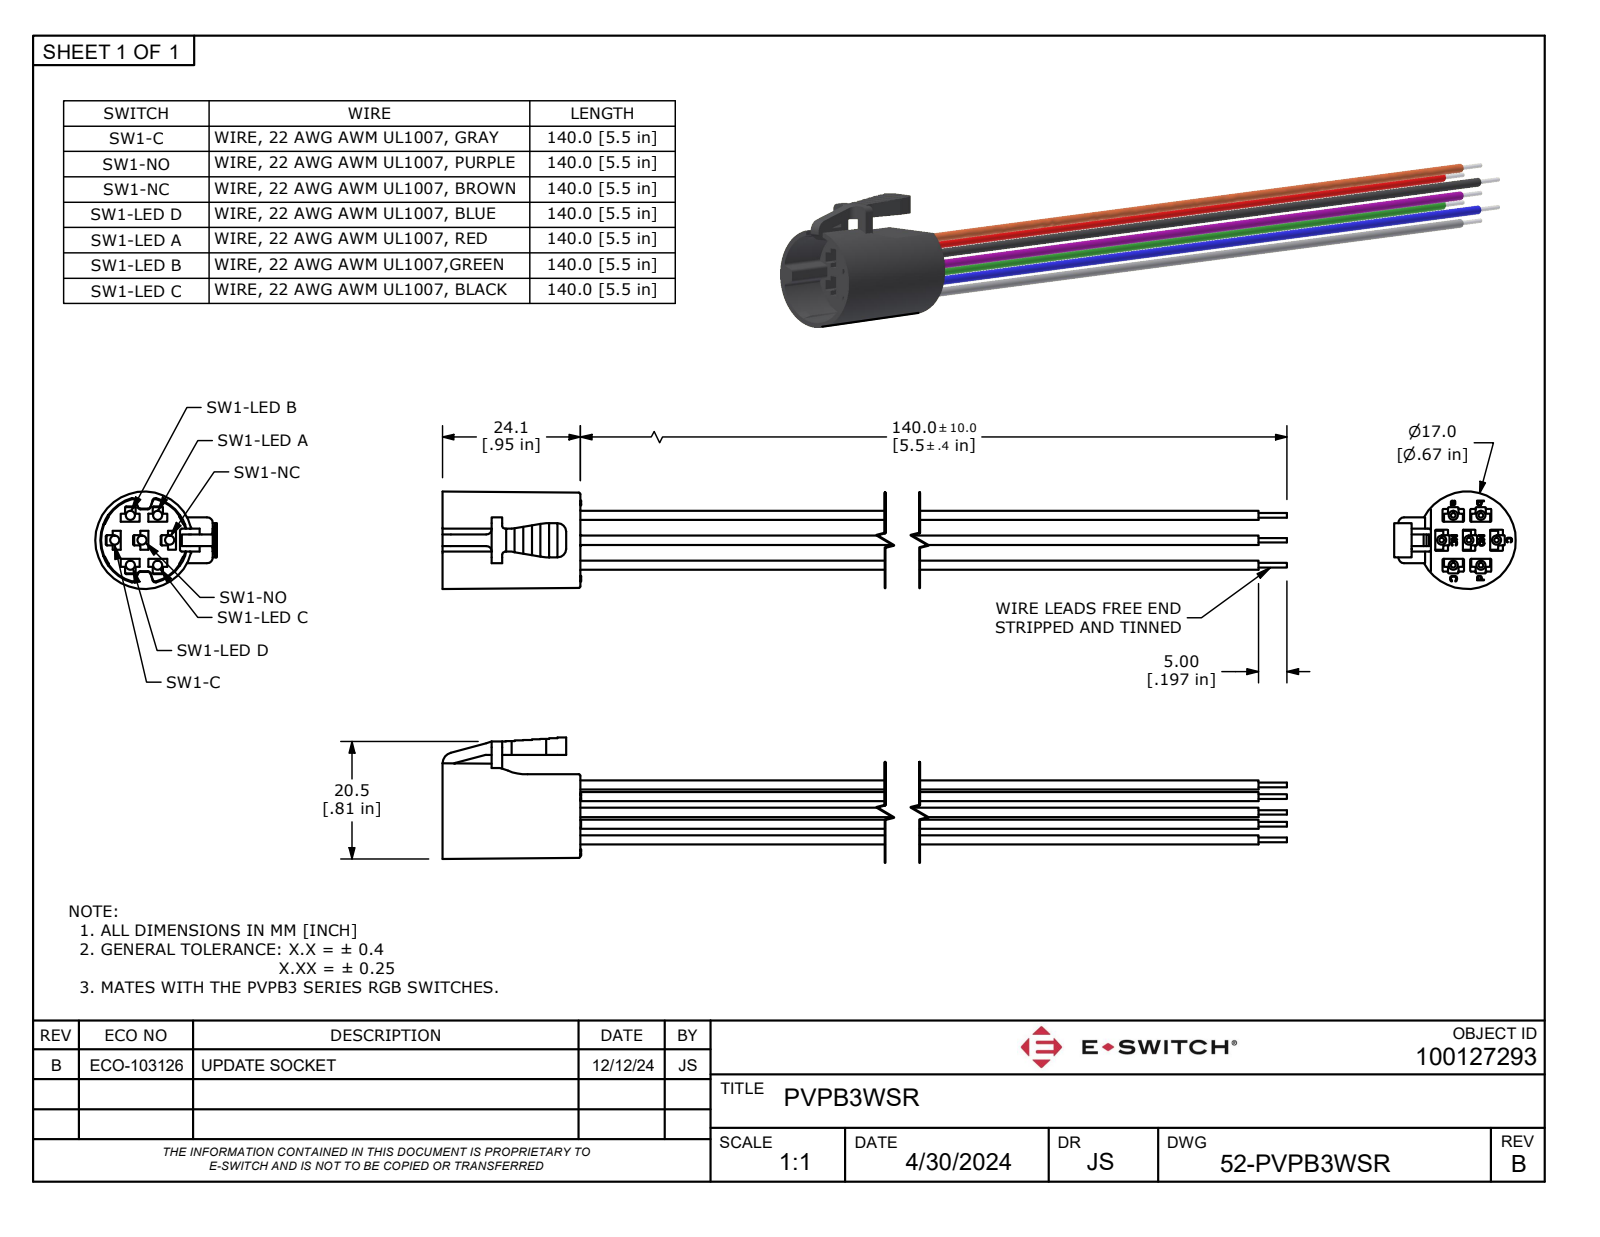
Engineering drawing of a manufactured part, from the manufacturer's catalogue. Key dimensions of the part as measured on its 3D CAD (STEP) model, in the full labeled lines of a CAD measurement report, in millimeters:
Part name (STEP PRODUCT): PVPB3WSR
STEP written by: Autodesk Inventor 2022 (AUTOMOTIVE_DESIGN)
Units: millimetres
Bodies: 8 solids, 737 faces (563 planar, 14 cylindrical, 160 other)
Overall size (bounding box): 164.1 × 21.2 × 17
Volume: 4 230 mm³ · Surface area: 8 600 mm²
Round bosses / shafts (diameter × count): ⌀1.6 ×7, ⌀0.8 ×7
Main face-to-face distances: 4.8, 15.5, 5, 3.7, 0.8, 4.4, 5.1, 1.4, 4, 2.2
